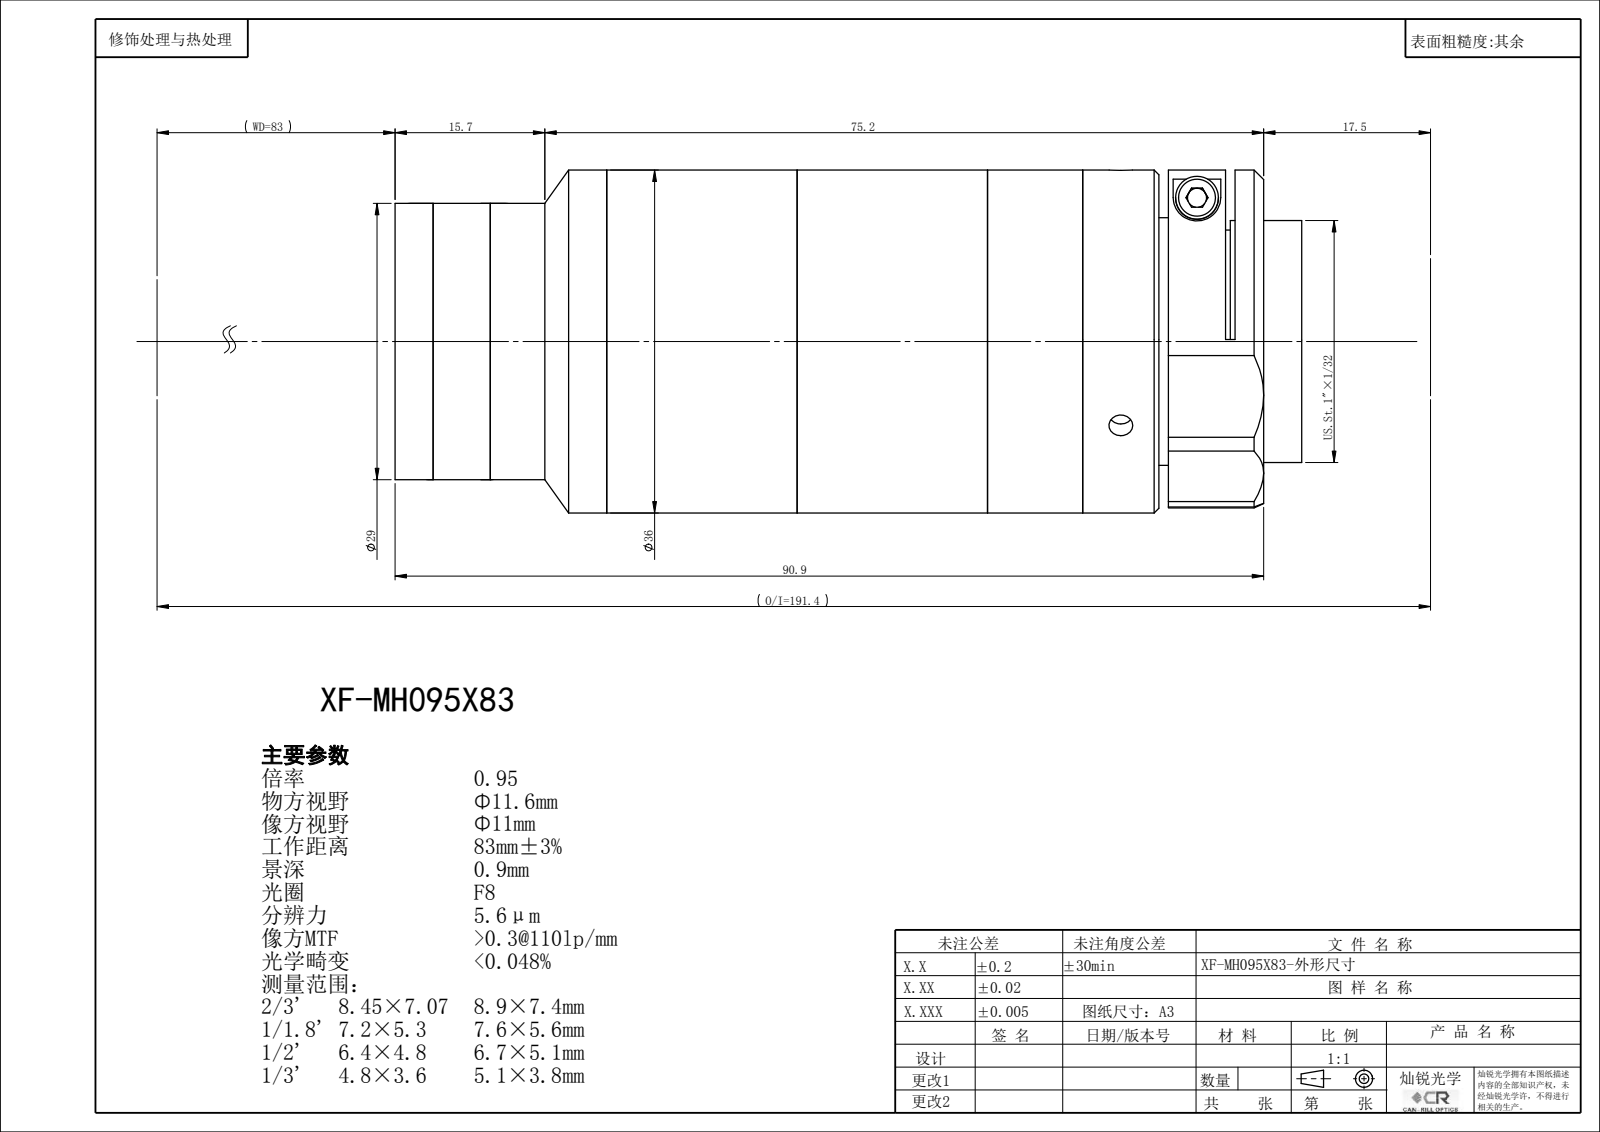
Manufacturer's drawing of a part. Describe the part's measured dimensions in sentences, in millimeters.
The part is named "XF-MH095X83". Its 3-D file was written by "SolidWorks 2022 (CONFIG_CONTROL_DESIGN)". It is 0 solids with 132 faces: 68 planar, 42 cylindrical and 22 other. Overall it measures 94.95 by 36.01 by 36 millimeters. Round holes: 3 of diameter 2.5, 1 of diameter 14, 1 of diameter 22.4, 1 of diameter 24, 1 of diameter 24.9, 1 of diameter 26. Round bosses or shafts: 1 of diameter 36, 1 of diameter 34, 1 of diameter 29, 1 of diameter 25.4. The main face-to-face distances are 18.71, 68.44, 87.15, 1.5, 85.65, 17.21, 10, 58.44, 27.21, 28.71.
